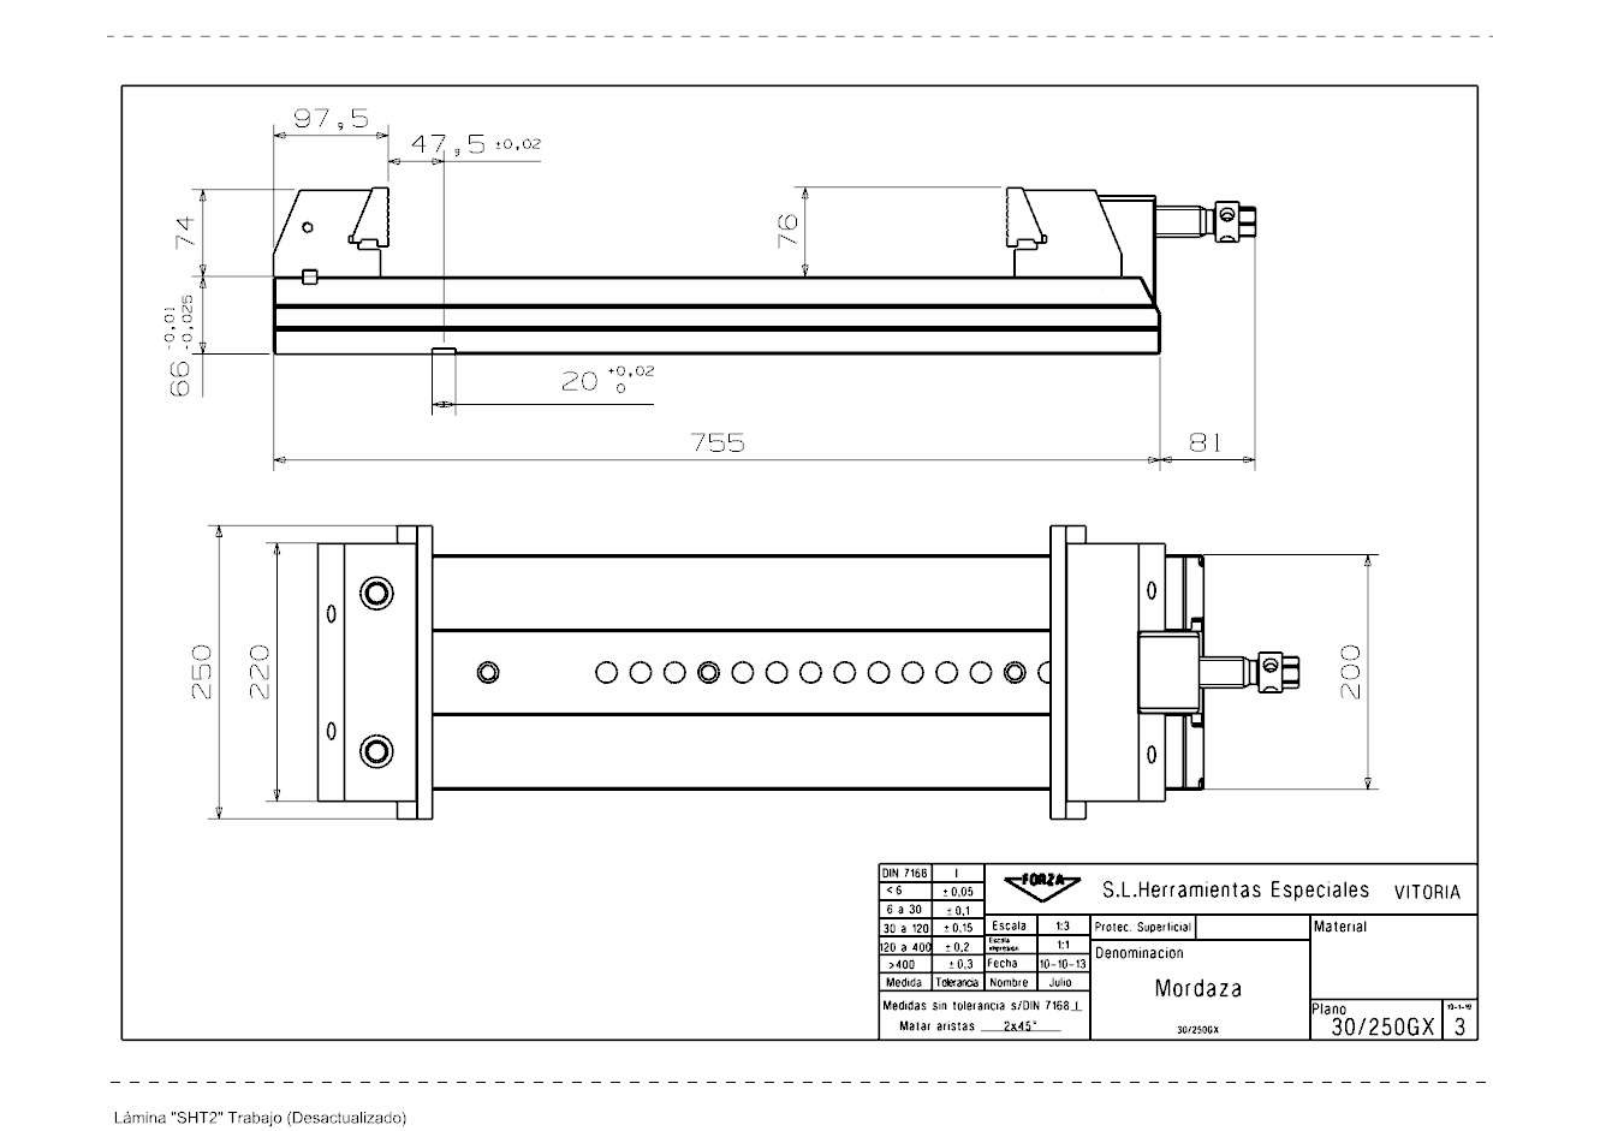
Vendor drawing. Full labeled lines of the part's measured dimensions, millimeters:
Part name (STEP PRODUCT): 30_250GX_Mordaza
STEP written by: SIEMENS PLM Software NX 11.0 (AUTOMOTIVE_DESIGN)
Units: millimetres
Bodies: 12 solids, 638 faces (470 planar, 103 cylindrical, 65 other)
Overall size (bounding box): 836 × 250 × 142
Volume: 10 680 000 mm³ · Surface area: 916 338 mm²
Round holes (diameter × count): ⌀5.19 ×6, ⌀19 ×5, ⌀9.5 ×4, ⌀15 ×4, ⌀18 ×4, ⌀8.78 ×3, ⌀10.58 ×3, ⌀12.38 ×3, ⌀13 ×3, ⌀6.5 ×2, ⌀6.99 ×2, ⌀8.5 ×2
Round bosses / shafts (diameter × count): ⌀34 ×1, ⌀33.8 ×1, ⌀26 ×1, ⌀20 ×1, ⌀16.5 ×1
Partial cylindrical surfaces — rounded edges, fillets, slot ends (radius × count): R10 ×8, R6.5 ×2, R9 ×1, R10.5 ×1, R12.5 ×1, R13.25 ×1
Main face-to-face distances: 66, 33.7, 32.3, 1.5, 64.5, 32.2, 145, 10, 65, 200
Hole centre spacings: 70, 20, 21, 27.31, 29, 30, 35.38, 46.32
